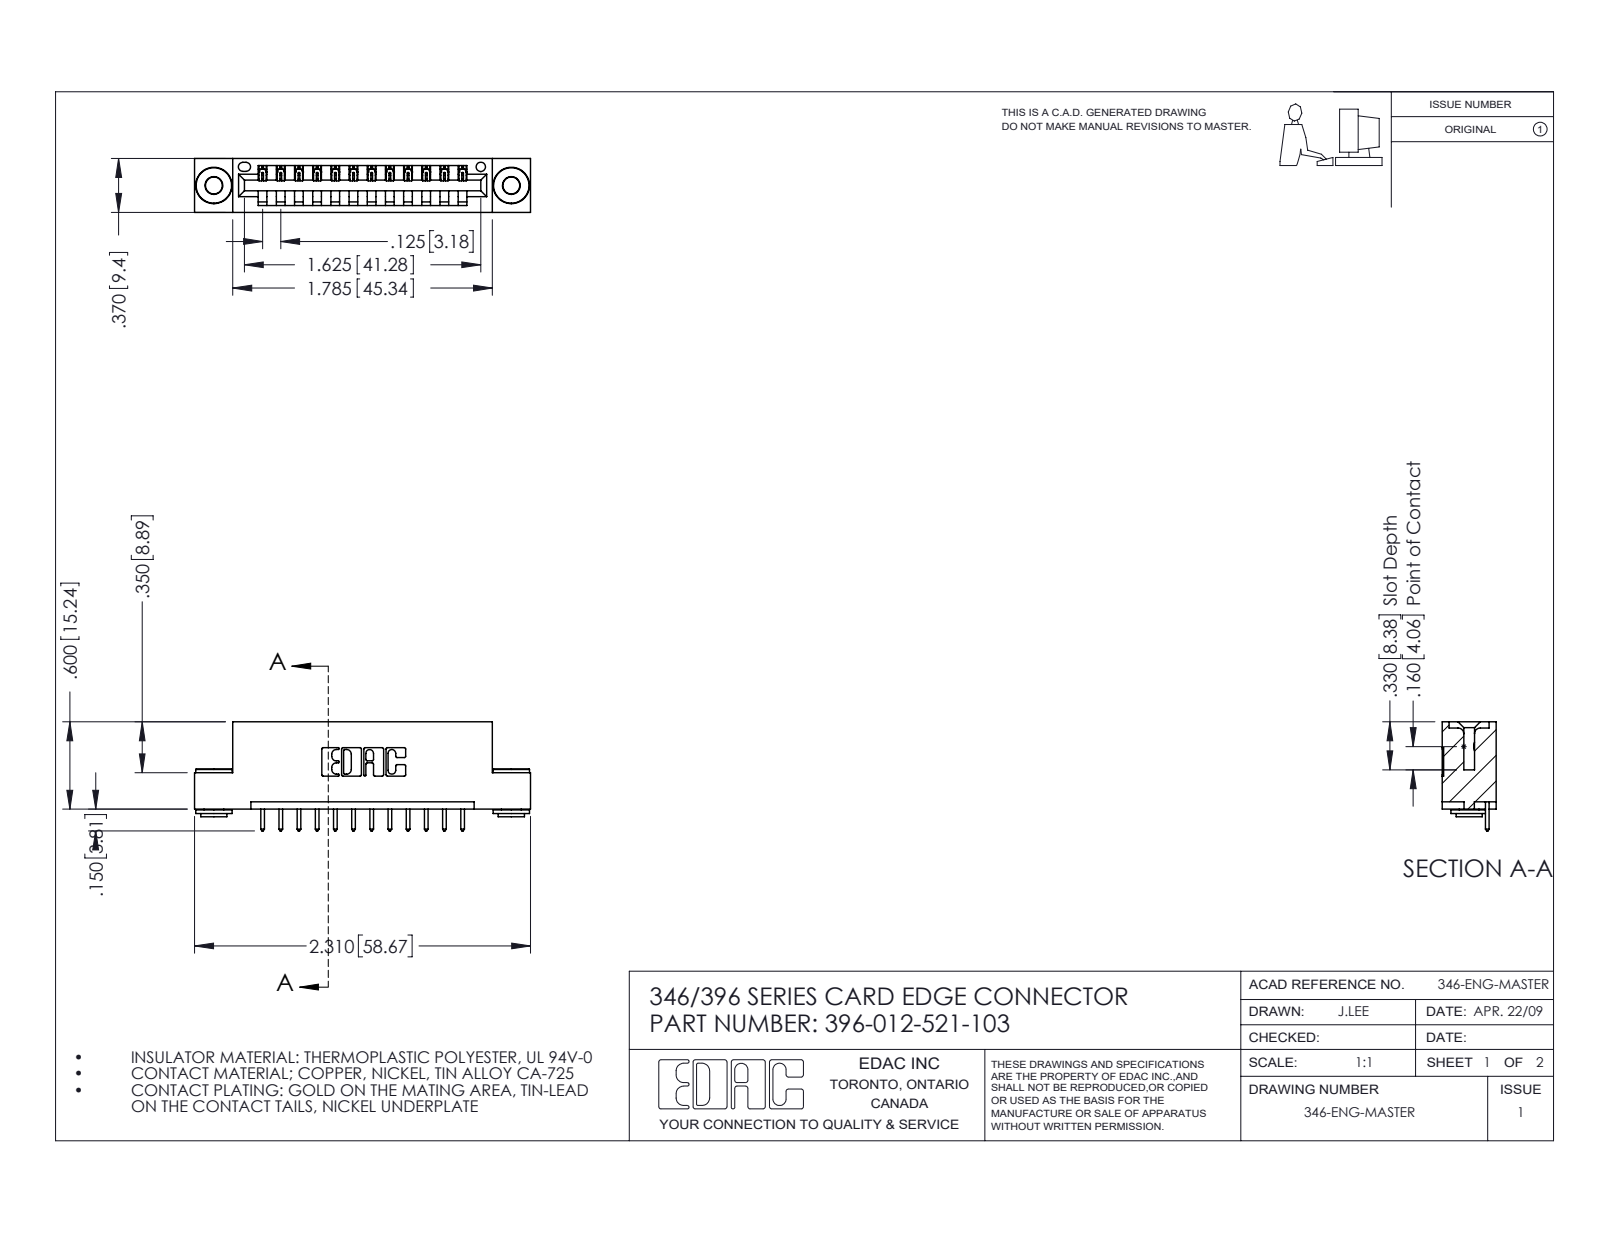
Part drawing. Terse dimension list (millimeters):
name: 396-012-521-103; 346 Part_Flush Mounting Lugs - 0.156 Dia-TH; 345-250-002_345-250-002-102; 345-292-001_345-293-121
written by: SolidWorks 2016 (CONFIG_CONTROL_DESIGN)
unit: mm
bodies: 15 solids, 856 faces (566 planar, 282 cylindrical, 8 other)
size: 58.7 × 19.1 × 9.4
volume: 5 390 mm³; area: 6 503 mm²
holes: 2× ⌀2.9, 2× ⌀4, 1× ⌀1.6
bosses: 2× ⌀6.4, 2× ⌀4.6, 2× ⌀3.5
rounds: 24× R0.2, 24× R0.3, 22× R0.3, 6× R0.2, 6× R0.8, 3× R0.7, 2× R0.8, 2× R1
face distances: 6.4, 1.2, 8.2, 9.4, 0.6, 3.8, 5.6, 2.5, 4.4, 1.8
hole spacings: 6.2, 46.7, 51.9
